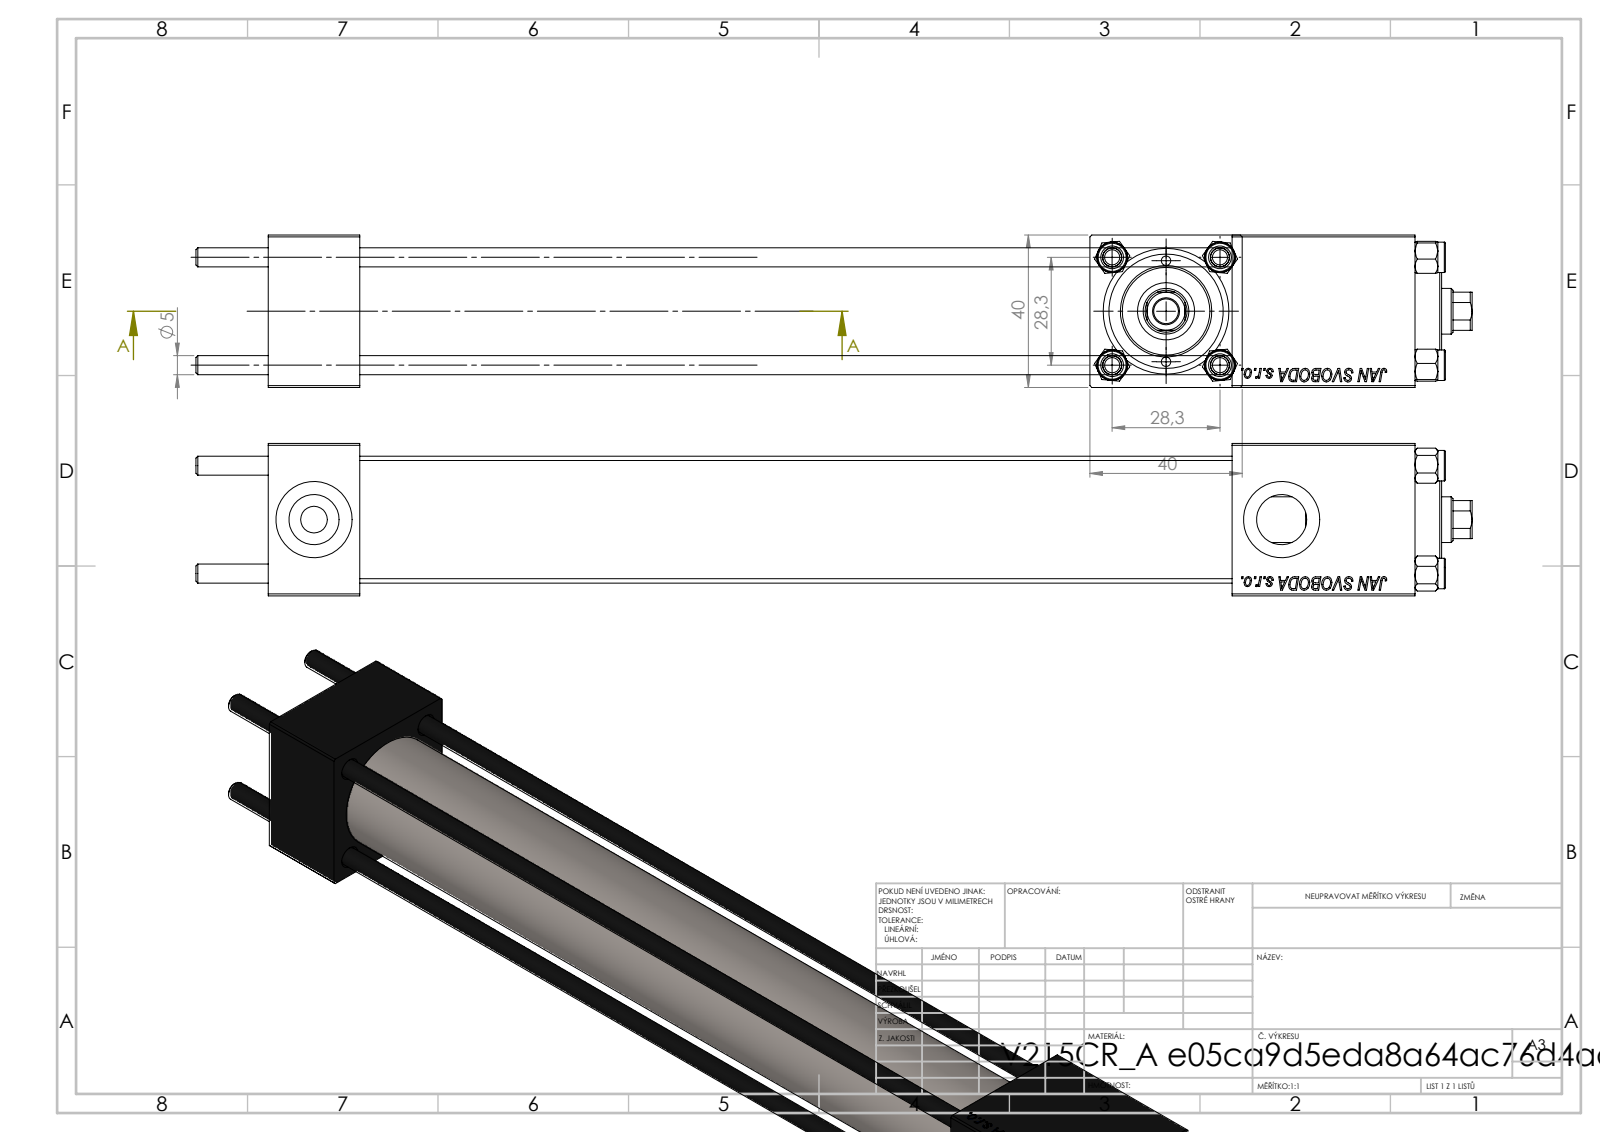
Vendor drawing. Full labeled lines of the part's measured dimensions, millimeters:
Part name (STEP PRODUCT): CR025_012_A_0_G_A_G_M_020_+#_##_TYCINKA; NUT_M5; V215_VC_A; V215CR_VCP (+1 more)
STEP written by: SolidWorks 2019 (CONFIG_CONTROL_DESIGN)
Units: millimetres
Bodies: 11 solids, 1137 faces (519 planar, 82 cylindrical, 536 other)
Overall size (bounding box): 335 × 40 × 40
Volume: 227 682 mm³ · Surface area: 109 266 mm²
Round holes (diameter × count): ⌀5 ×4, ⌀20 ×3, ⌀2.5 ×2, ⌀7 ×2, ⌀13.16 ×2, ⌀6.5 ×1, ⌀12 ×1, ⌀15 ×1, ⌀25 ×1, ⌀30 ×1
Round bosses / shafts (diameter × count): ⌀8 ×4, ⌀31 ×1, ⌀24 ×1
Partial cylindrical surfaces — rounded edges, fillets, slot ends (radius × count): R5.5 ×1
Main face-to-face distances: 40, 24, 272.3, 248.3, 301, 277, 28.7, 253, 229, 19.3
Hole centre spacings: 14.18, 20.01, 28.3, 30.84, 13.25, 40.02, 26.5, 254
